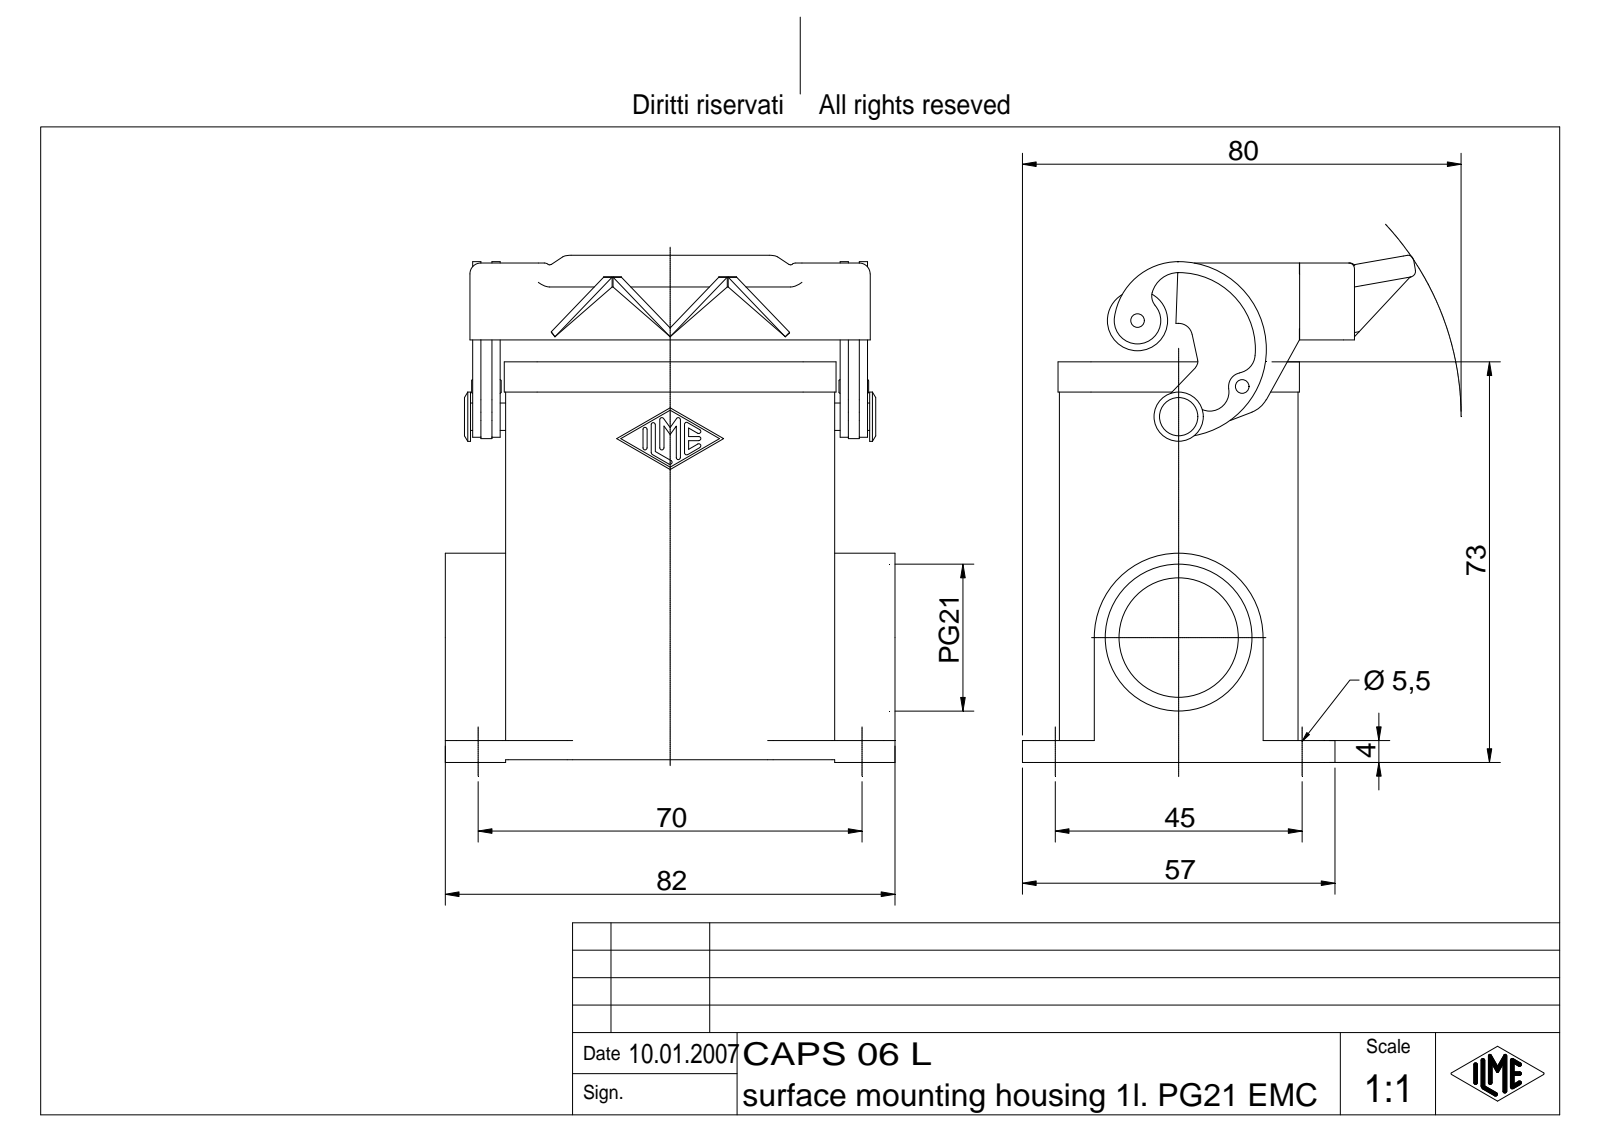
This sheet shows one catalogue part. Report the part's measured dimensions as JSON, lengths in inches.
{"part_name": "CAPS 06 L", "step_written_by": "Autodesk Inventor 7 (AUTOMOTIVE_DESIGN)", "units": "inches", "bodies": {"solids": 1, "faces": 492, "planar": 157, "cylindrical": 139, "other": 196}, "overall_size": [3.639, 3.228, 2.823], "volume_in3": 5.685, "surface_area_in2": 73.99, "round_holes": [[0.217, 2], [0.098, 1], [0.857, 1], [1.054, 1]], "round_bosses_or_shafts": [[0.433, 1], [0.354, 1], [0.197, 1], [0.118, 1], [0.079, 1]], "partial_cylinders_radius": [[0.079, 24], [0.015, 14], [0.236, 8], [0.039, 7], [0.118, 4], [0.059, 3], [0.098, 3], [0.138, 2]], "face_to_face_distances": [0.118, 1.594, 1.713, 0.157, 1.476, 0.138, 0.128, 0.03, 2.362, 2.717], "hole_center_spacings": [1.858, 3.276]}
